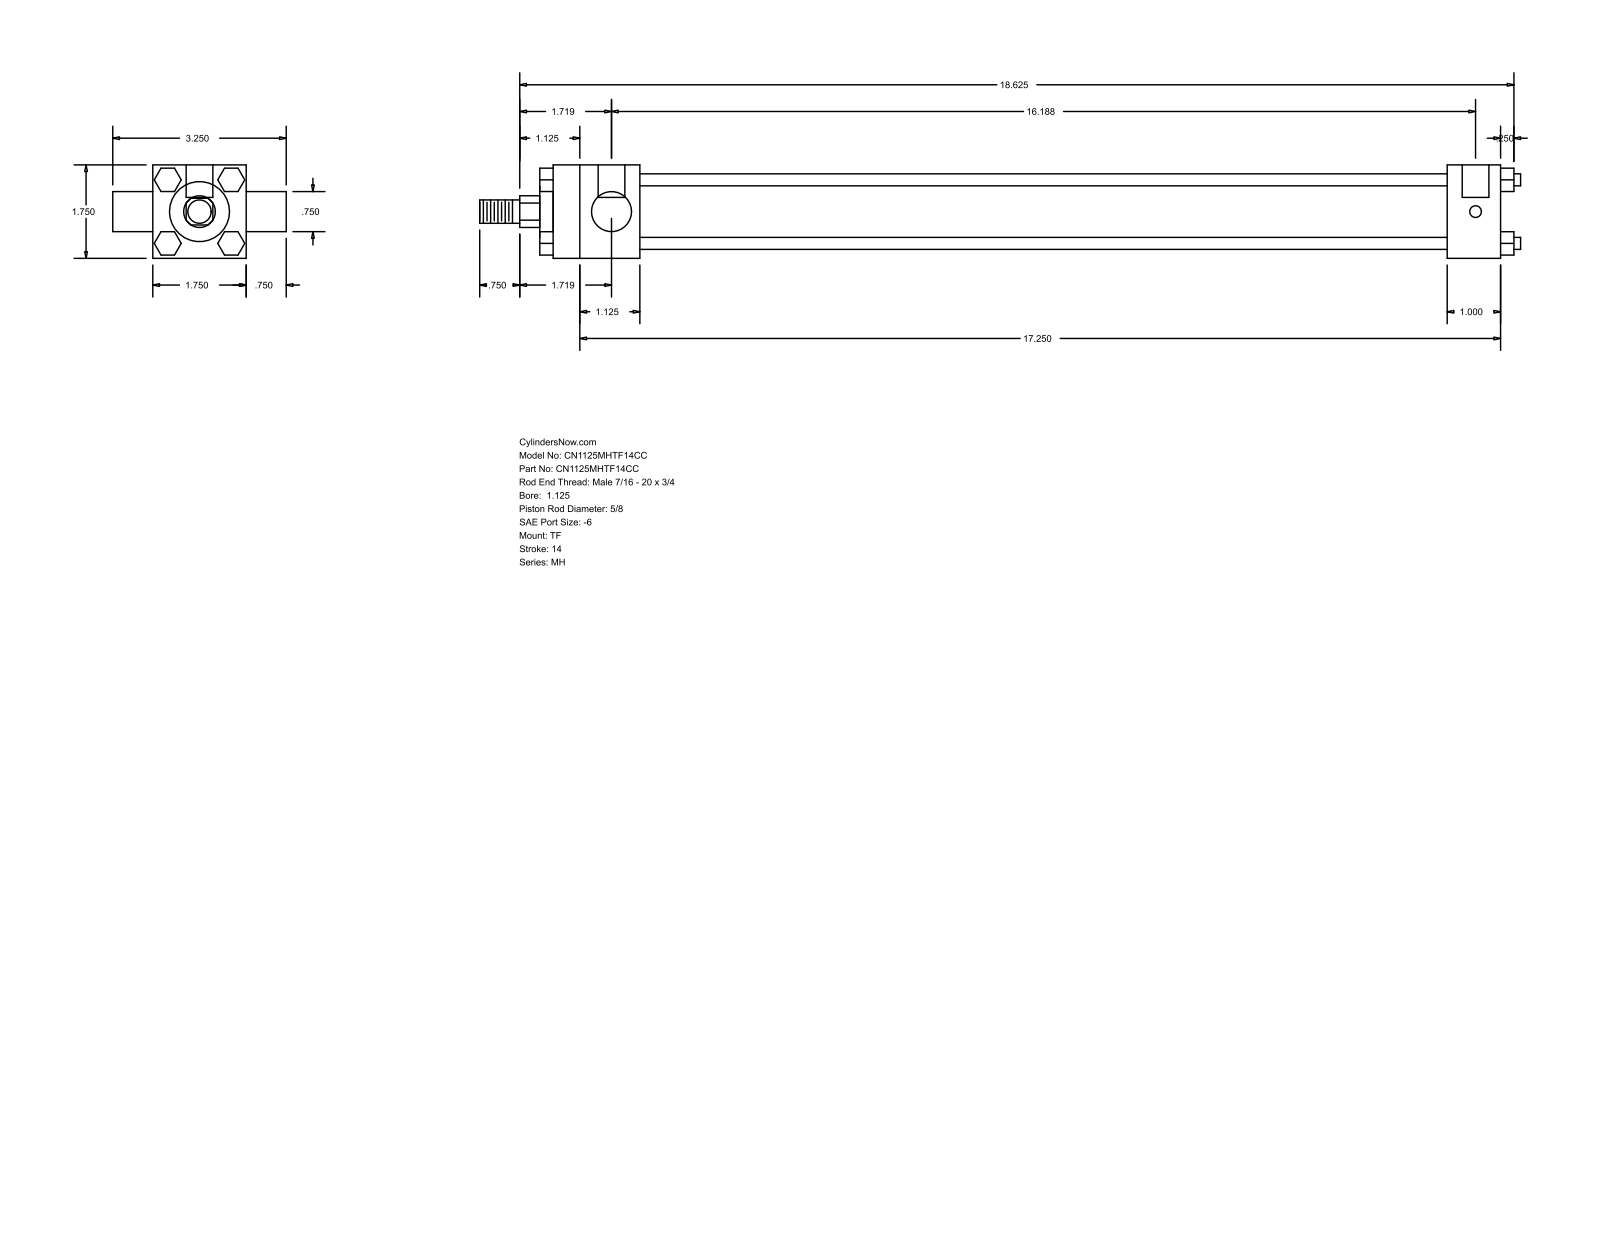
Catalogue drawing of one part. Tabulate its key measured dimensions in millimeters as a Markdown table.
| quantity | value |
| --- | --- |
| part name | MH_TF__0112_0.625 |
| STEP written by | GSSL Pune (CONFIG_CONTROL_DESIGN) |
| units | millimeters |
| bodies | 0 solids, 120 faces (92 planar, 28 cylindrical, 0 other) |
| overall size | 495.3 × 82.55 × 44.45 |
| round holes (diameter × count) | 5.56 × 3, 12.7 × 2 |
| round bosses / shafts (diameter × count) | 5.71 × 4, 34.92 × 1, 28.57 × 1, 19.05 × 1, 15.88 × 1, 11.11 × 1 |
| partial cylindrical surfaces (radius × count) | 7.54 × 1 |
| main face-to-face distances | 44.46, 11.11, 384.17, 409.58, 25.41, 41.27, 425.44, 450.85, 47.62, 6.35 |
| hole center spacings | 3.17, 407.99, 411.16 |
